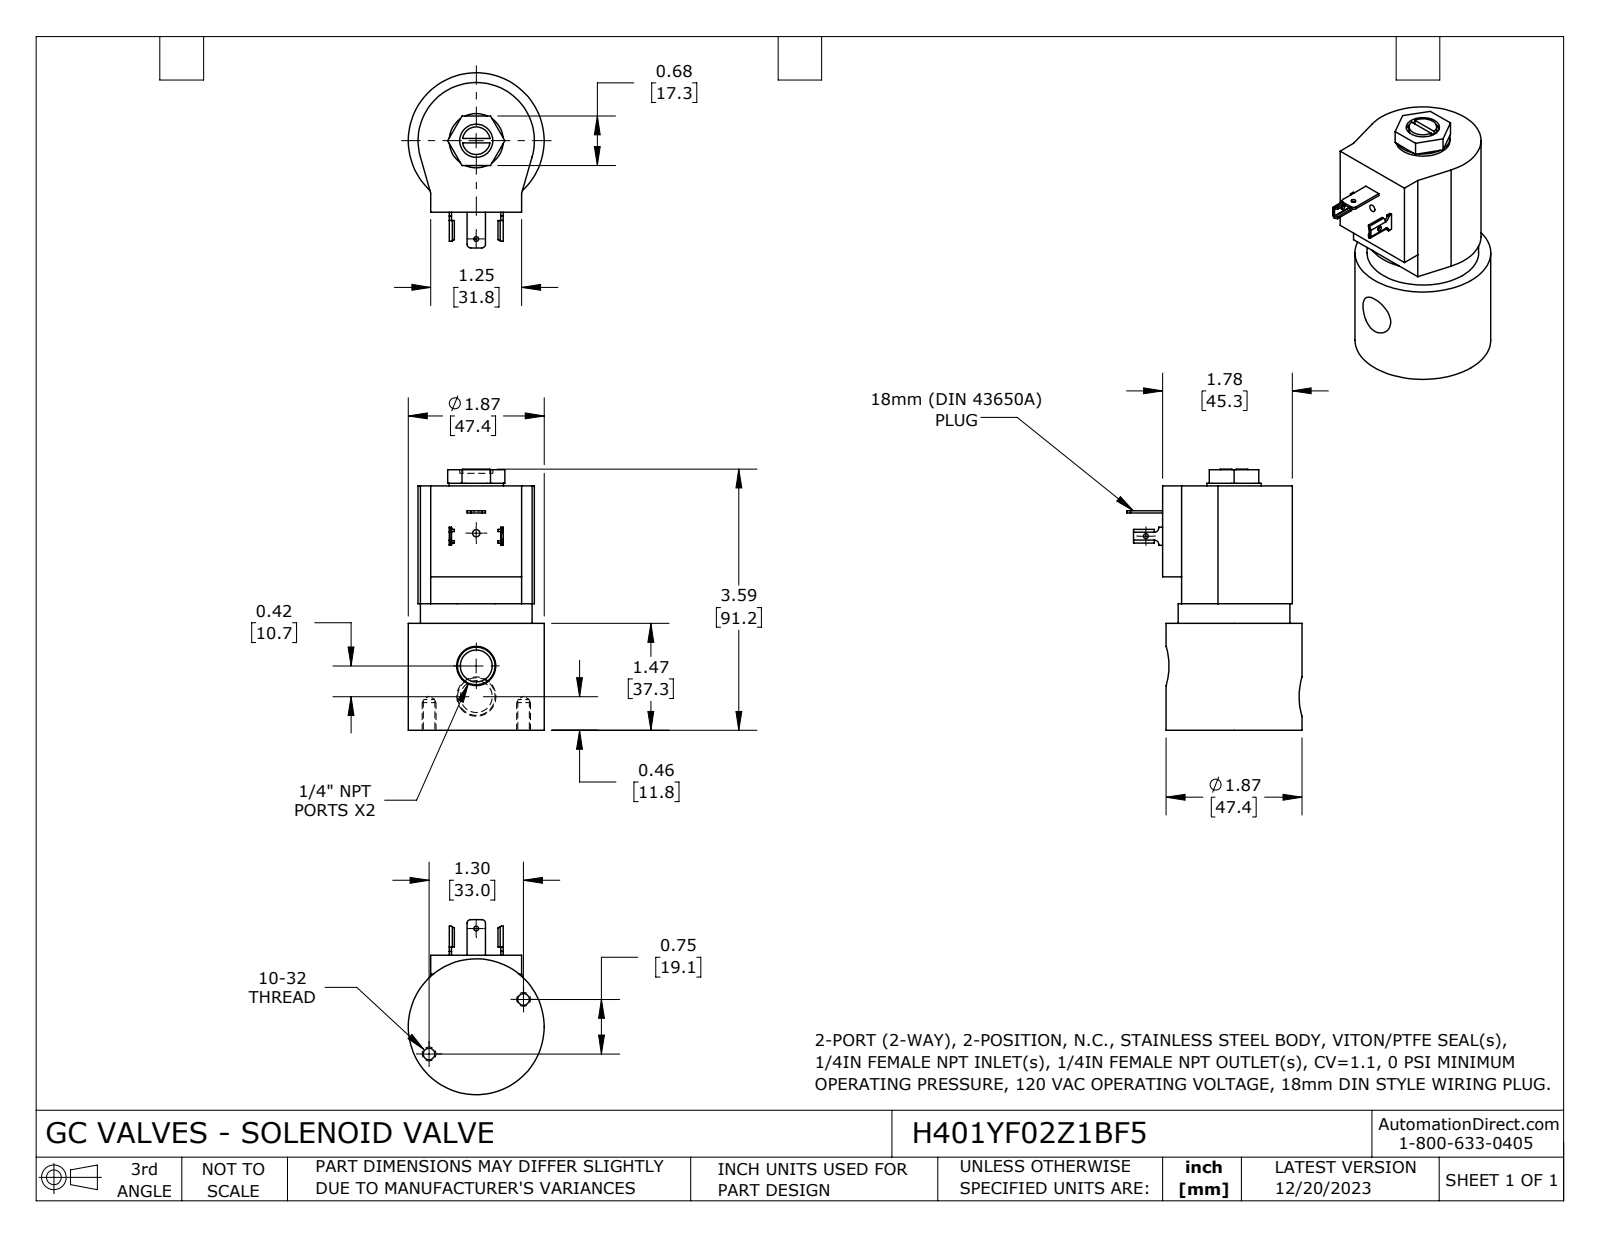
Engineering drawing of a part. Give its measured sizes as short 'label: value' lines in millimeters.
name: H401YF02Z1BF5
written by: SolidWorks 2023 (CONFIG_CONTROL_DESIGN)
unit: mm
bodies: 1 solid, 132 faces (75 planar, 43 cylindrical, 14 other)
size: 91.2 × 61.1 × 47.4
volume: 133 000 mm³; area: 18 830 mm²
holes: 2× ⌀4, 2× ⌀11.1, 1× ⌀1.7, 1× ⌀1.7, 1× ⌀2.5, 1× ⌀11.6
bosses: 1× ⌀47.4, 1× ⌀39, 1× ⌀18.9, 1× ⌀9.7
rounds: 4× R0.2, 4× R1, 2× R1.3, 2× R1.5, 1× R20.3
face distances: 85.3, 37.3, 48, 6.6, 53.6, 16.3, 31.8, 31.8, 91, 53.7
hole spacings: 19.1, 10.7, 29.7, 34.3, 38.1, 46.3, 46.8, 57
